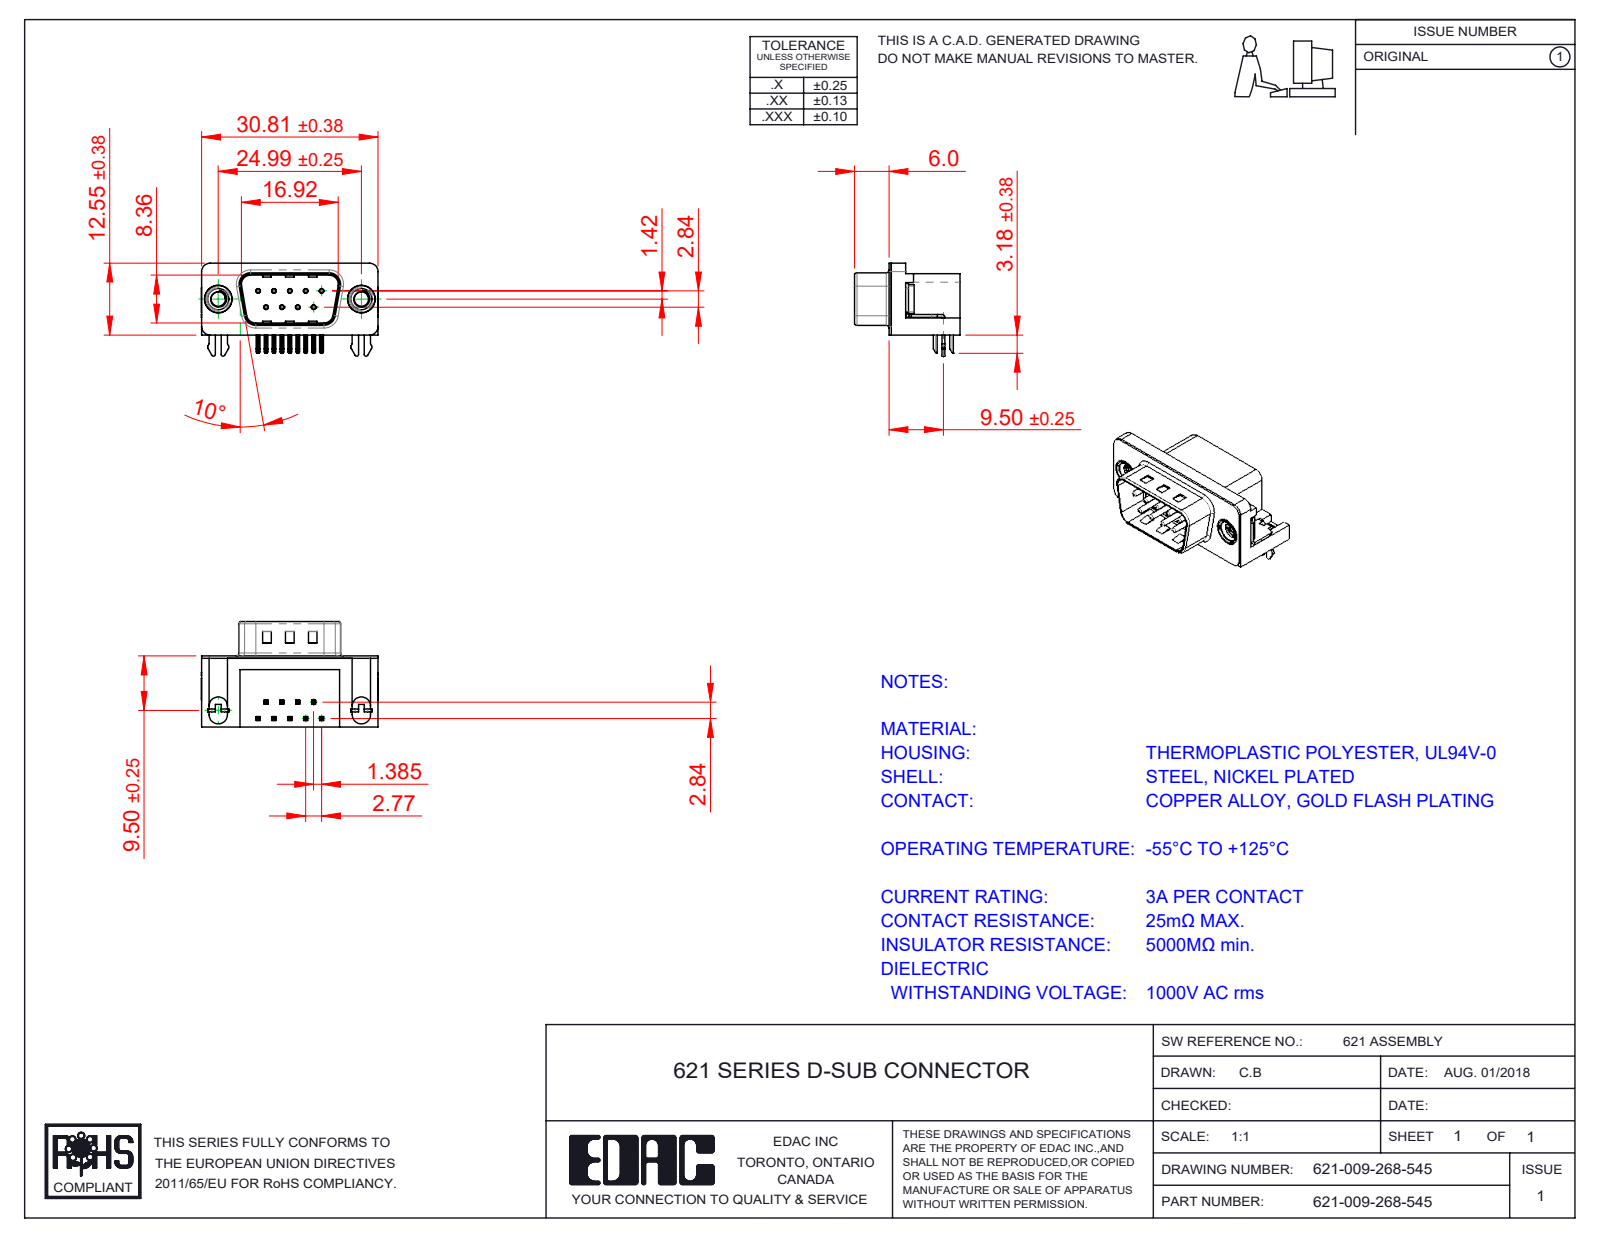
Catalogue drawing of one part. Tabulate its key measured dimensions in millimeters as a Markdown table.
| quantity | value |
| --- | --- |
| part name | 621 Housing_9 Socket; 621 4 Prong Board Lock; 621 Contact Top; 621-009-268-545 (+3 more) |
| STEP written by | SolidWorks 2016 (CONFIG_CONTROL_DESIGN) |
| units | millimeters |
| bodies | 15 solids, 1111 faces (615 planar, 325 cylindrical, 171 other) |
| overall size | 30.89 × 18.4 × 16.25 |
| volume | 3 250 mm³ |
| surface area | 4 499 mm² |
| round holes (diameter × count) | 0.35 × 9, 0.8 × 9, 2 × 2, 2.5 × 2, 4 × 2, 4.8 × 2, 5 × 2 |
| round bosses / shafts (diameter × count) | 0.75 × 9, 4.9 × 2, 4.75 × 2, 3.9 × 2, 3 × 2 |
| partial cylindrical surfaces (radius × count) | 0.25 × 48, 0.12 × 18, 1 × 16, 0.5 × 9, 1.5 × 8, 1.6 × 8, 0.9 × 4, 2 × 4 |
| main face-to-face distances | 0.4, 12, 12.4, 10.35, 2.9, 9.5, 2.5, 2.1, 0.35, 10.7 |
| hole center spacings | 3.16, 2.77, 5.54, 5.03, 5.04, 8.31, 7.48, 7.49 |
